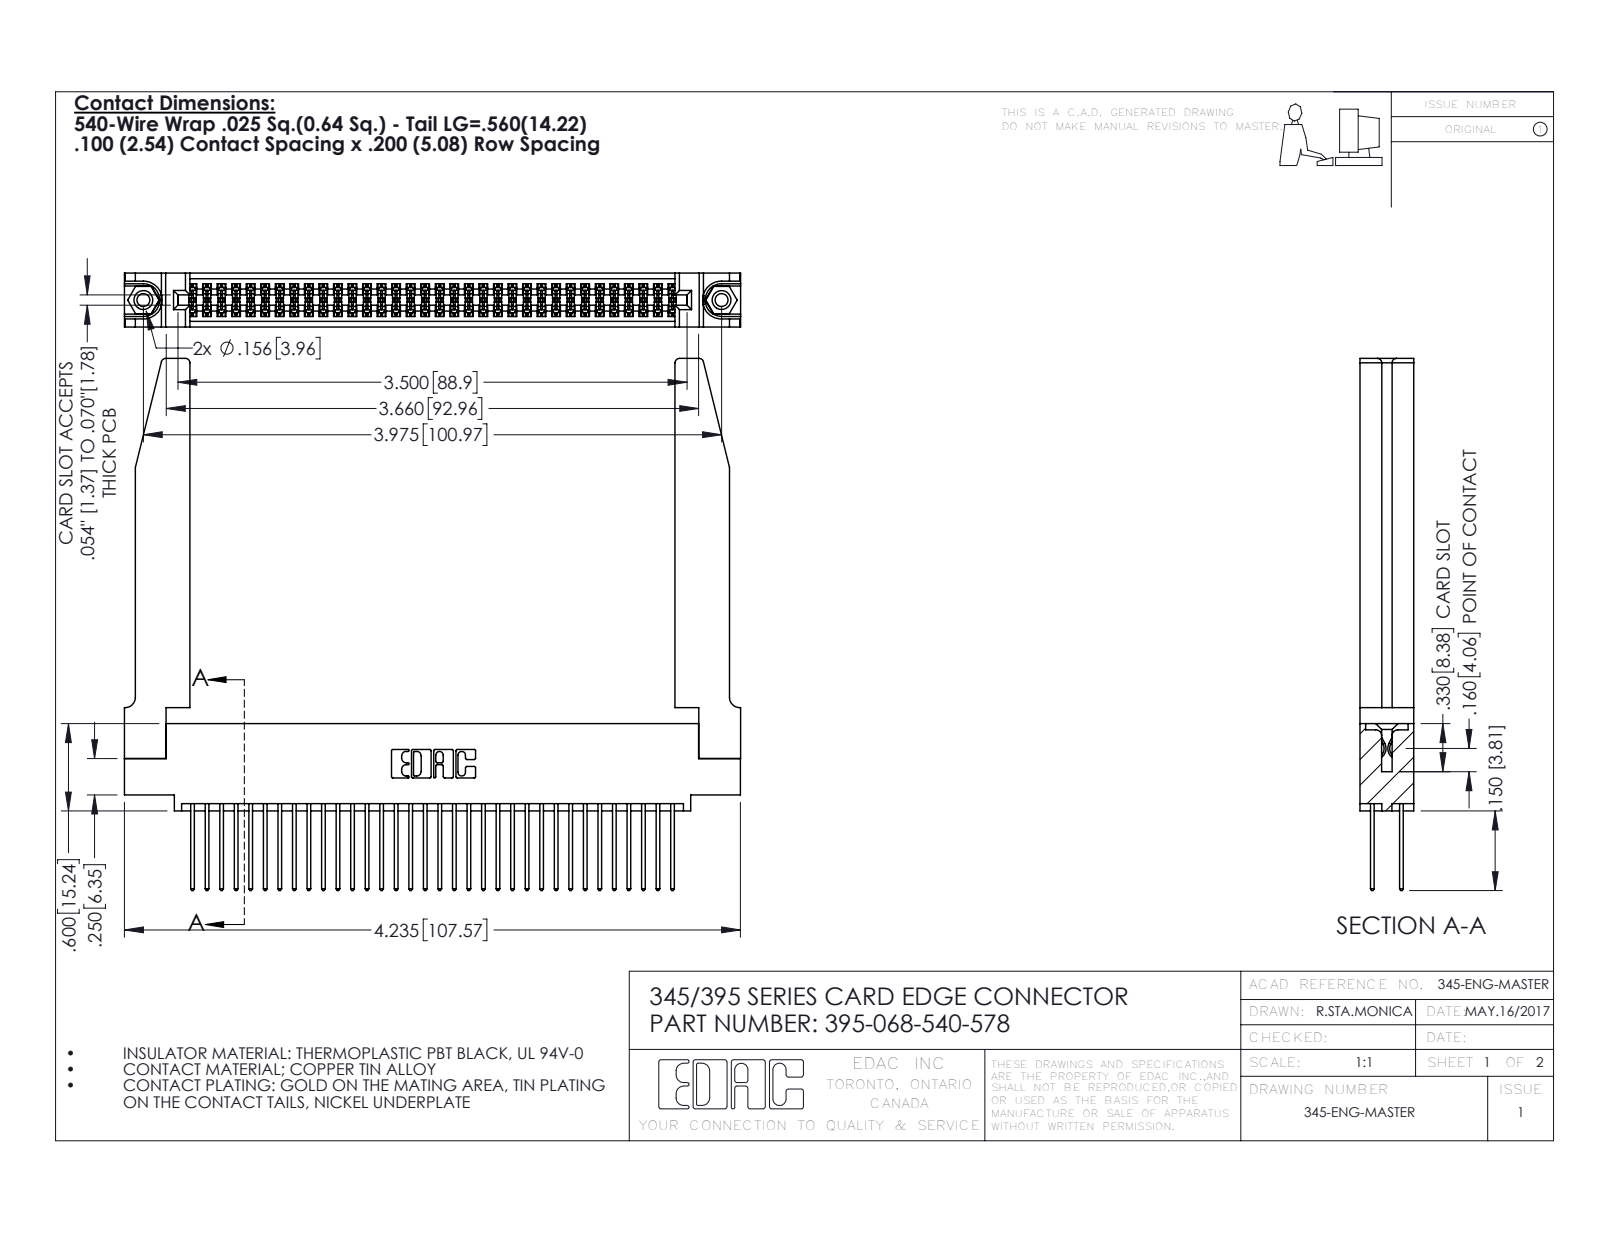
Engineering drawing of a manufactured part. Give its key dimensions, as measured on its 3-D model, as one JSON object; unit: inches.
{"part_name": "345 Part_0.110 Offset - 0.156 Dia-TH; 395-068-540-578; 345-250-001_345-250-001-102; 345-220-078_345-220-078 (+1 more)", "step_written_by": "SolidWorks 2016 (CONFIG_CONTROL_DESIGN)", "units": "inches", "bodies": {"solids": 73, "faces": 3764, "planar": 2470, "cylindrical": 1242, "other": 52}, "overall_size": [4.236, 3.657, 0.37], "volume_in3": 1.119, "surface_area_in2": 36.56, "round_holes": [[0.089, 2], [0.125, 2], [0.156, 2], [0.064, 1]], "round_bosses_or_shafts": [[0.155, 2]], "partial_cylinders_radius": [[0.006, 102], [0.01, 68], [0.01, 22], [0.03, 8], [0.007, 6], [0.031, 6], [0.026, 3], [0.014, 2]], "face_to_face_distances": [0.072, 0.298, 0.37, 0.2, 0.098, 0.272, 0.025, 0.225, 0.175, 0.15], "hole_center_spacings": [0.27, 3.74, 3.975]}
